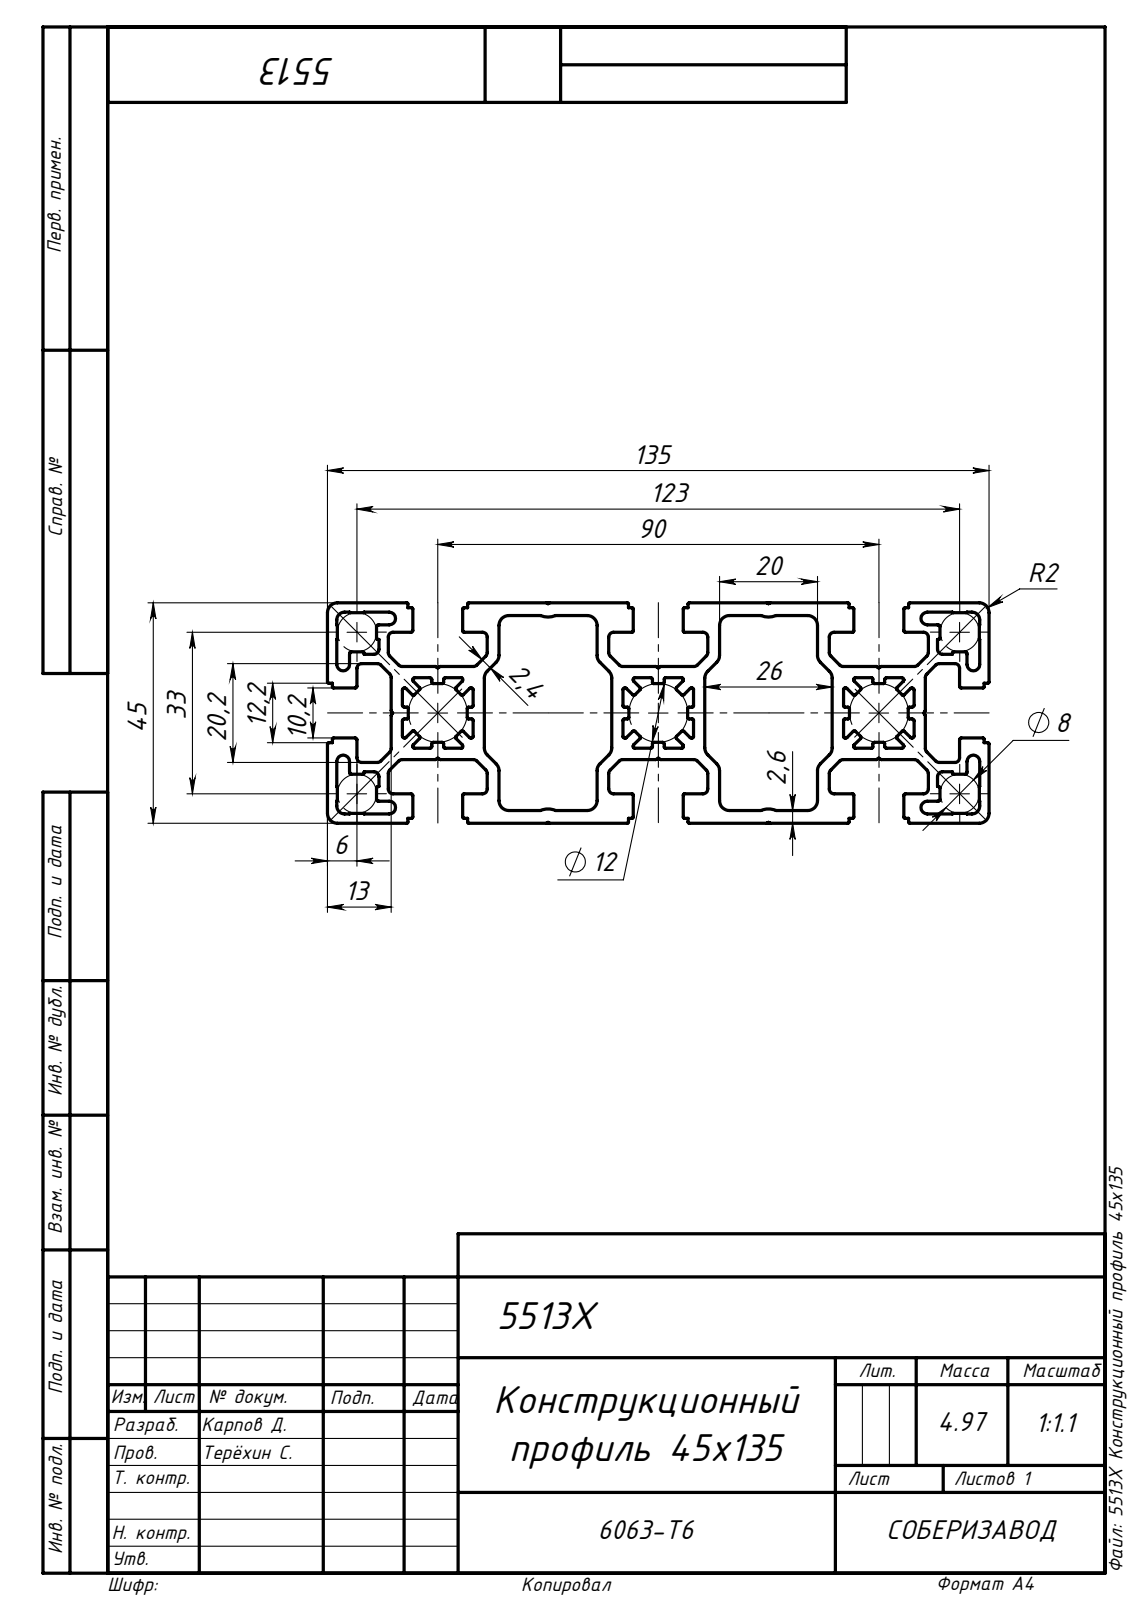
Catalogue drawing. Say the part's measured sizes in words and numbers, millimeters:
The part is named "5513X Конструкционный профиль 45х135". Its 3-D file was written by "SolidWorks 2019 (AUTOMOTIVE_DESIGN)". It is 1 solid with 722 faces: 382 planar, 340 cylindrical and 0 other. Overall it measures 1000 by 135 by 45 millimeters. Its volume is 1 841 000 cubic millimeters and its surface area 1 352 000 square millimeters. Partial cylindrical surfaces (rounded edges, fillets, slot ends): 112 of radius 0.25, 80 of radius 0.3, 52 of radius 1, 28 of radius 2, 24 of radius 0.4, 8 of radius 0.35, 8 of radius 1.3, 4 of radius 1.6. The main face-to-face distances are 45, 32, 13, 14.6, 19, 4.4, 26, 2.6, 10.4, 11.1.
